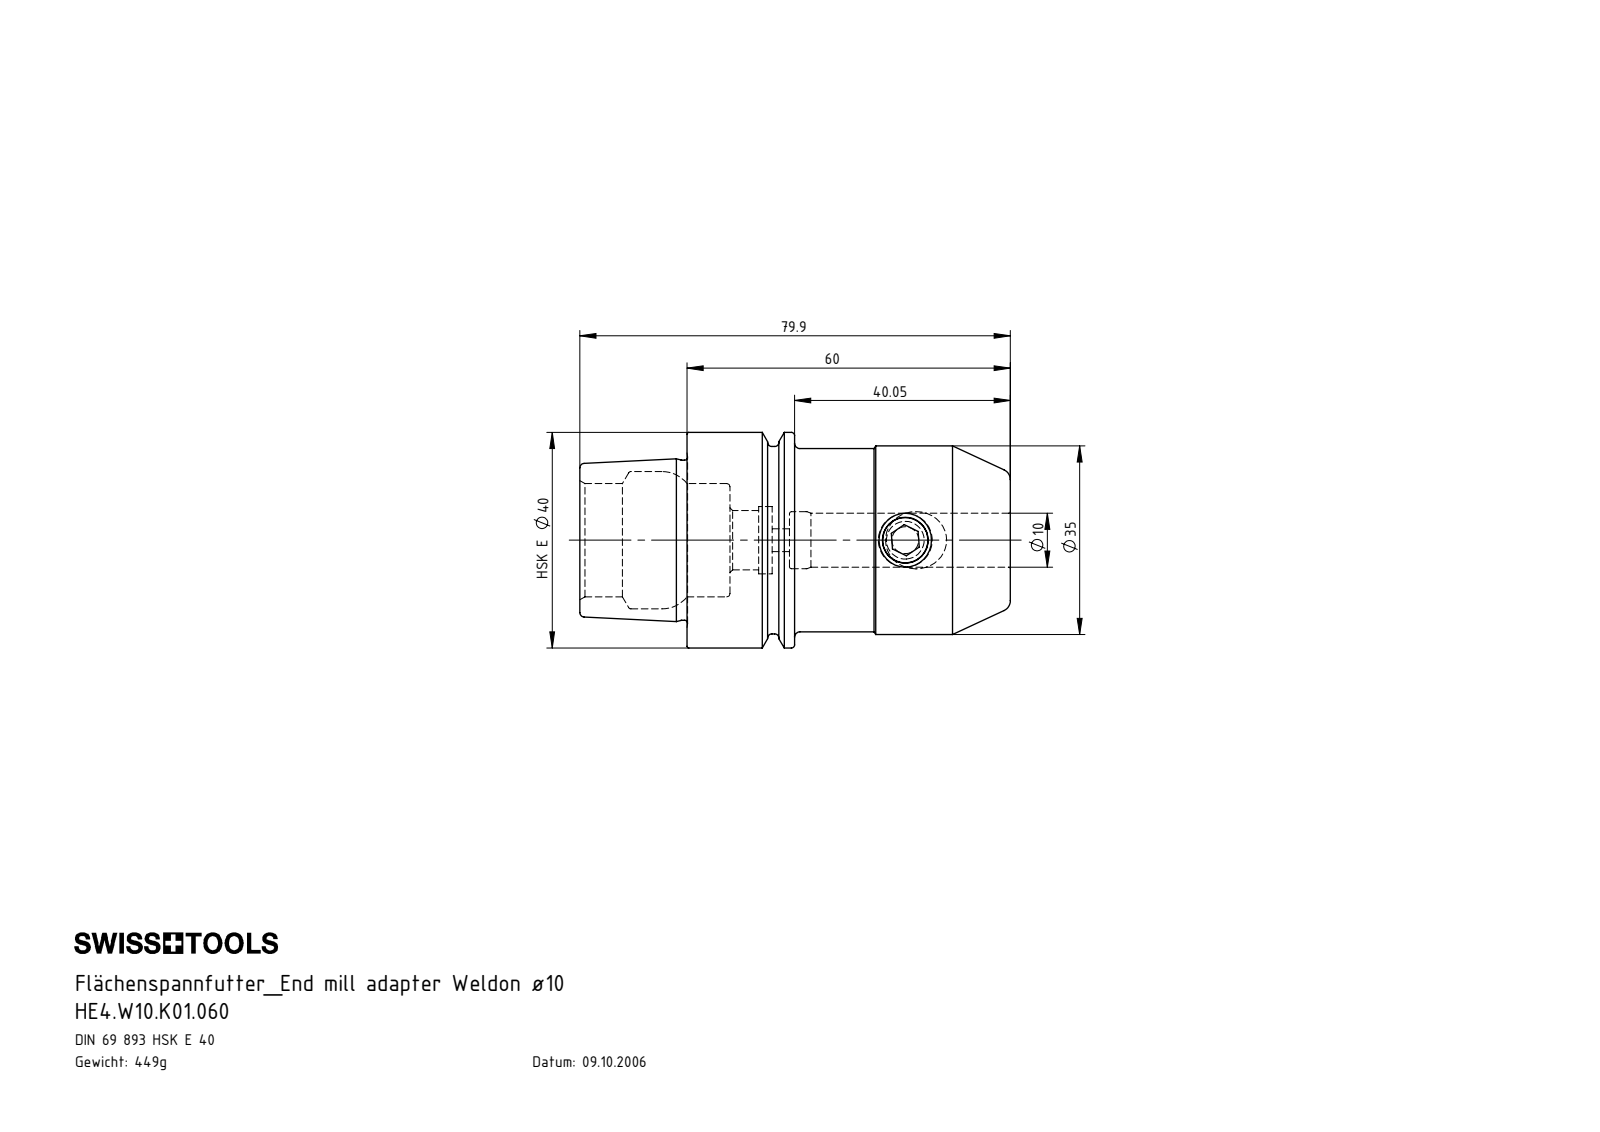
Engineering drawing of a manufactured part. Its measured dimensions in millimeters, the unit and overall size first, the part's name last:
Units: millimetres
Overall size (bounding box): 79.9 × 40 × 40
Round holes (diameter × count): ⌀4.2 ×1, ⌀8.5 ×1, ⌀10 ×1, ⌀10.6 ×1, ⌀11 ×1, ⌀12.5 ×1, ⌀21 ×1, ⌀25.5 ×1
Round bosses / shafts (diameter × count): ⌀40 ×1, ⌀35 ×1, ⌀34.75 ×1, ⌀34 ×1, ⌀29.71 ×1, ⌀10 ×1
Main face-to-face distances: 60, 7.95, 52.05, 19.9, 27.85, 79.9, 39.85, 19.95, 12, 40.05
Volume: 57 217 mm³ · Surface area: 15 461 mm²
Bodies: 2 solids, 113 faces (19 planar, 32 cylindrical, 62 other)
Part name (STEP PRODUCT): HE4.W10.K01.060; W10-ER1.001.012; HE4-W10.K01.060_B_Fertigbearbeitung
STEP written by: SolidWorks 2012 (AUTOMOTIVE_DESIGN)
